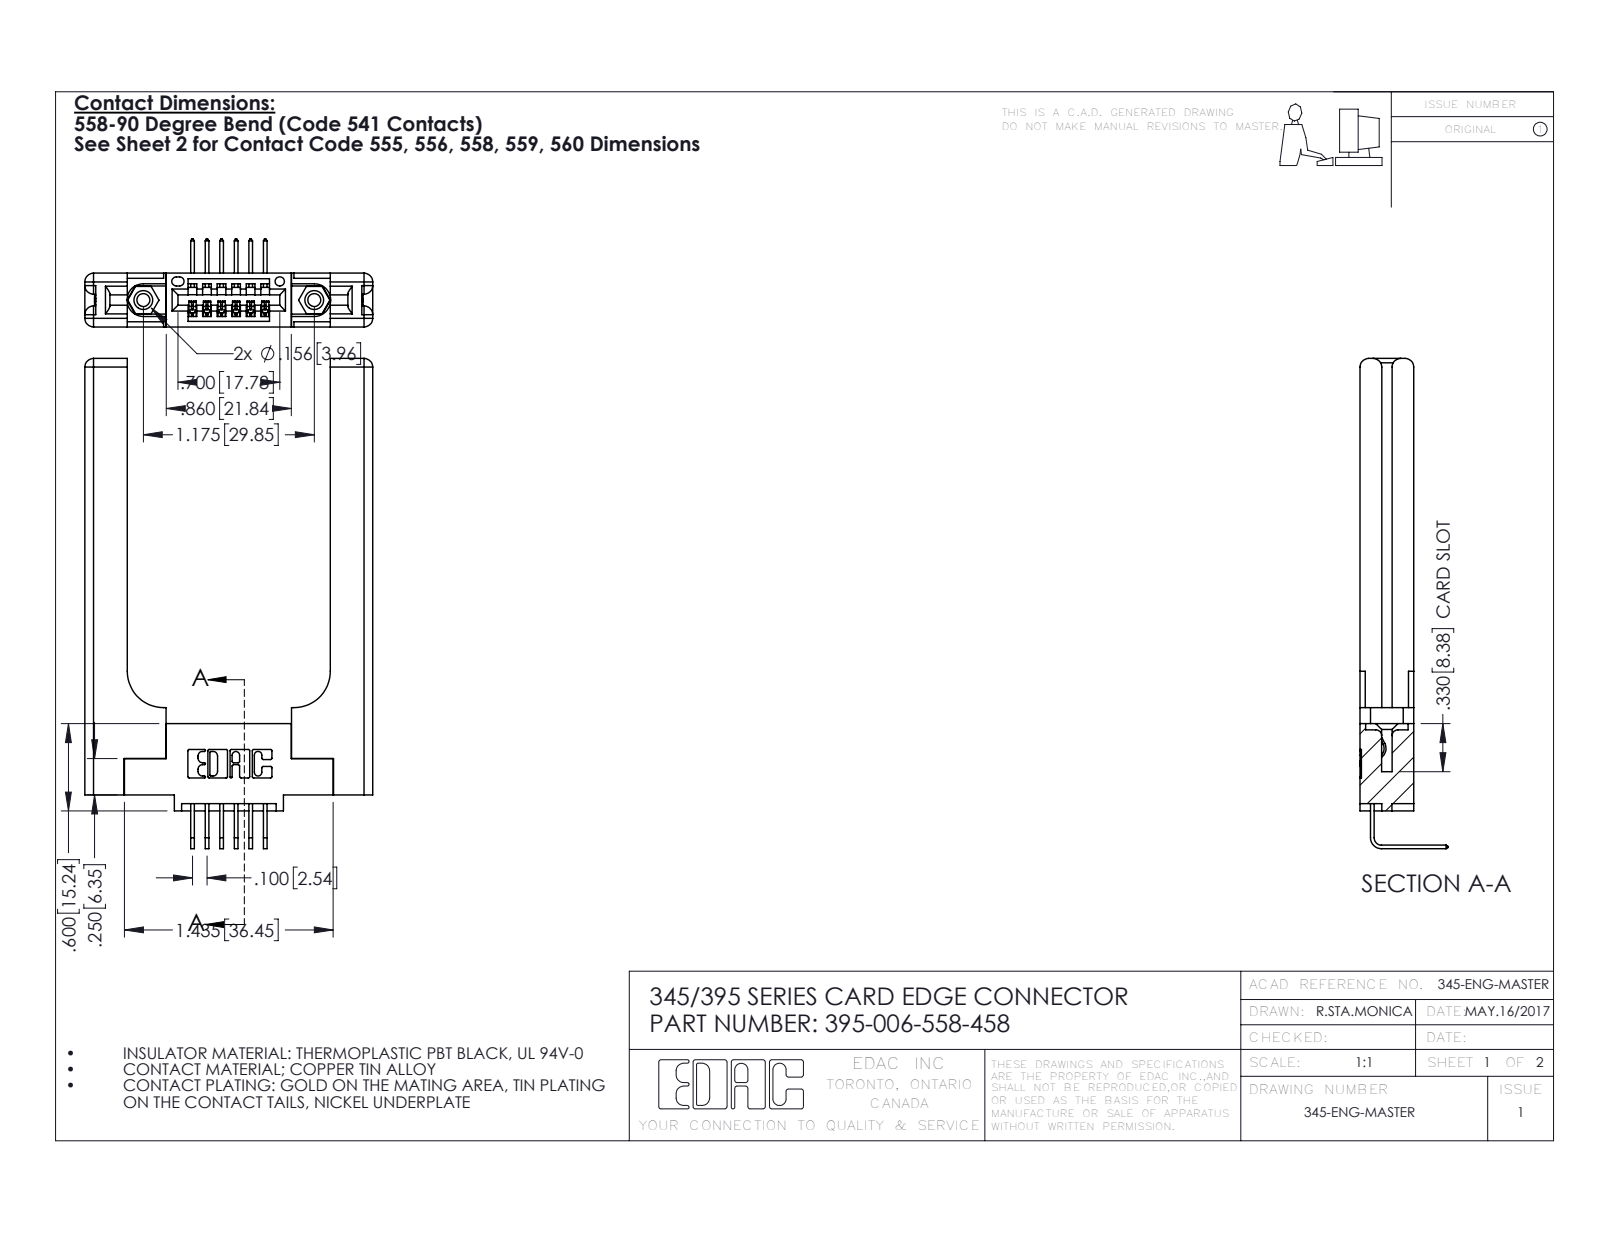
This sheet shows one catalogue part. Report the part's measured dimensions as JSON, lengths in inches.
{"part_name": "345-292-001_558 Tail - 2; 345-250-001_345-250-001-102; 395-006-558-458; 345-220-058_345-220-058 (+1 more)", "step_written_by": "SolidWorks 2016 (CONFIG_CONTROL_DESIGN)", "units": "inches", "bodies": {"solids": 11, "faces": 746, "planar": 484, "cylindrical": 202, "other": 60}, "overall_size": [3.369, 1.979, 0.605], "volume_in3": 0.789, "surface_area_in2": 16.89, "round_holes": [[0.089, 2], [0.125, 2], [0.156, 2], [0.064, 1]], "round_bosses_or_shafts": [[0.155, 2]], "partial_cylinders_radius": [[0.01, 22], [0.06, 16], [0.006, 12], [0.007, 6], [0.031, 6], [0.026, 3], [0.03, 2], [0.031, 2]], "face_to_face_distances": [0.37, 0.15, 0.22, 0.072, 1.396, 0.077, 0.148, 0.298, 0.071, 0.292], "hole_center_spacings": [0.27, 0.946, 1.175]}
